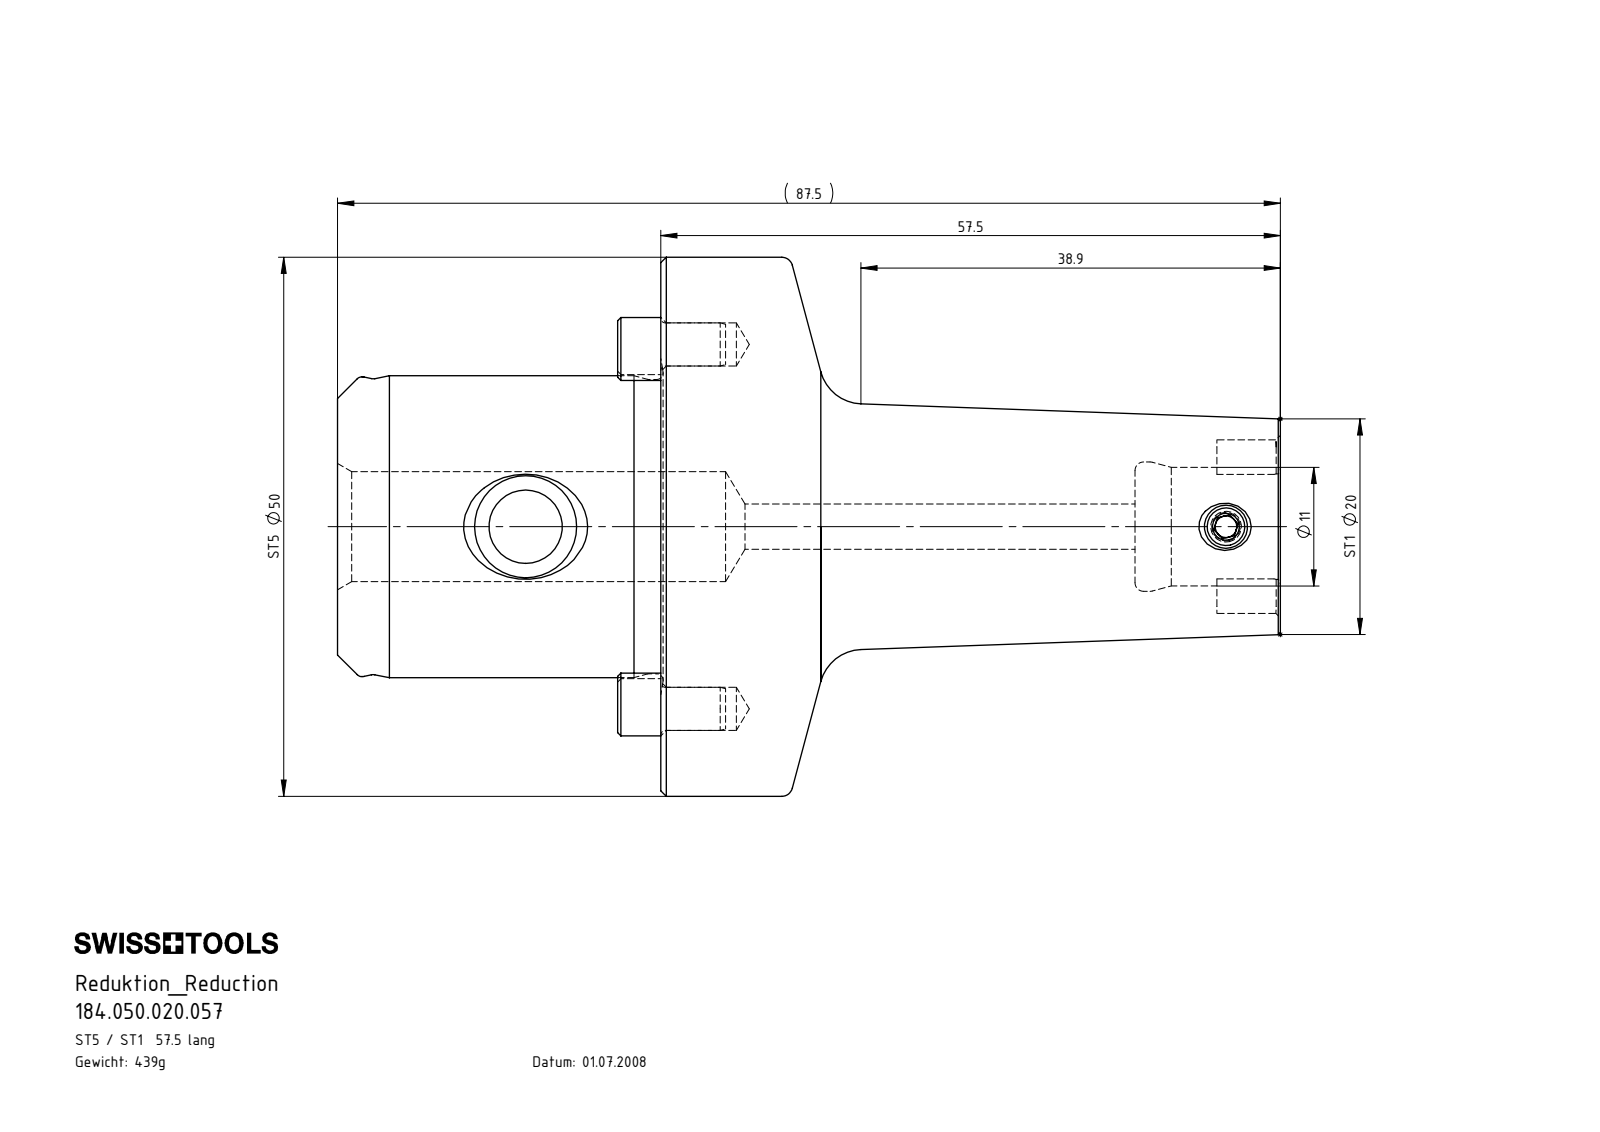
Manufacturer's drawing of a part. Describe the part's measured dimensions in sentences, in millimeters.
The part is named "ST5-ST1.K01.057; ST1-ER1.001.005_A; ST5-ER2.001.010_A; ST5-ST1.K01.057_B". Its 3-D file was written by "SolidWorks 2017 (CONFIG_CONTROL_DESIGN)". It is 4 solids with 172 faces: 32 planar, 47 cylindrical and 93 other. Overall it measures 87.5 by 50 by 50 millimeters. Its volume is 55 892 cubic millimeters and its surface area 14 008 square millimeters. Round holes: 2 of diameter 4, 1 of diameter 2, 1 of diameter 3.5, 1 of diameter 4.2, 1 of diameter 6.8, 1 of diameter 10.2, 1 of diameter 11, 1 of diameter 12. Round bosses or shafts: 1 of diameter 50, 1 of diameter 28, 1 of diameter 27.8, 1 of diameter 27.3, 1 of diameter 4. Partial cylindrical surfaces (rounded edges, fillets, slot ends): 4 of radius 0.5, 2 of radius 1.3, 2 of radius 4.47, 2 of radius 14.05. The main face-to-face distances are 30, 87.5, 57.5, 74, 44, 13.5, 26, 4, 48, 61.5. The hole center spacings are 16.9, 33.8, 65.
